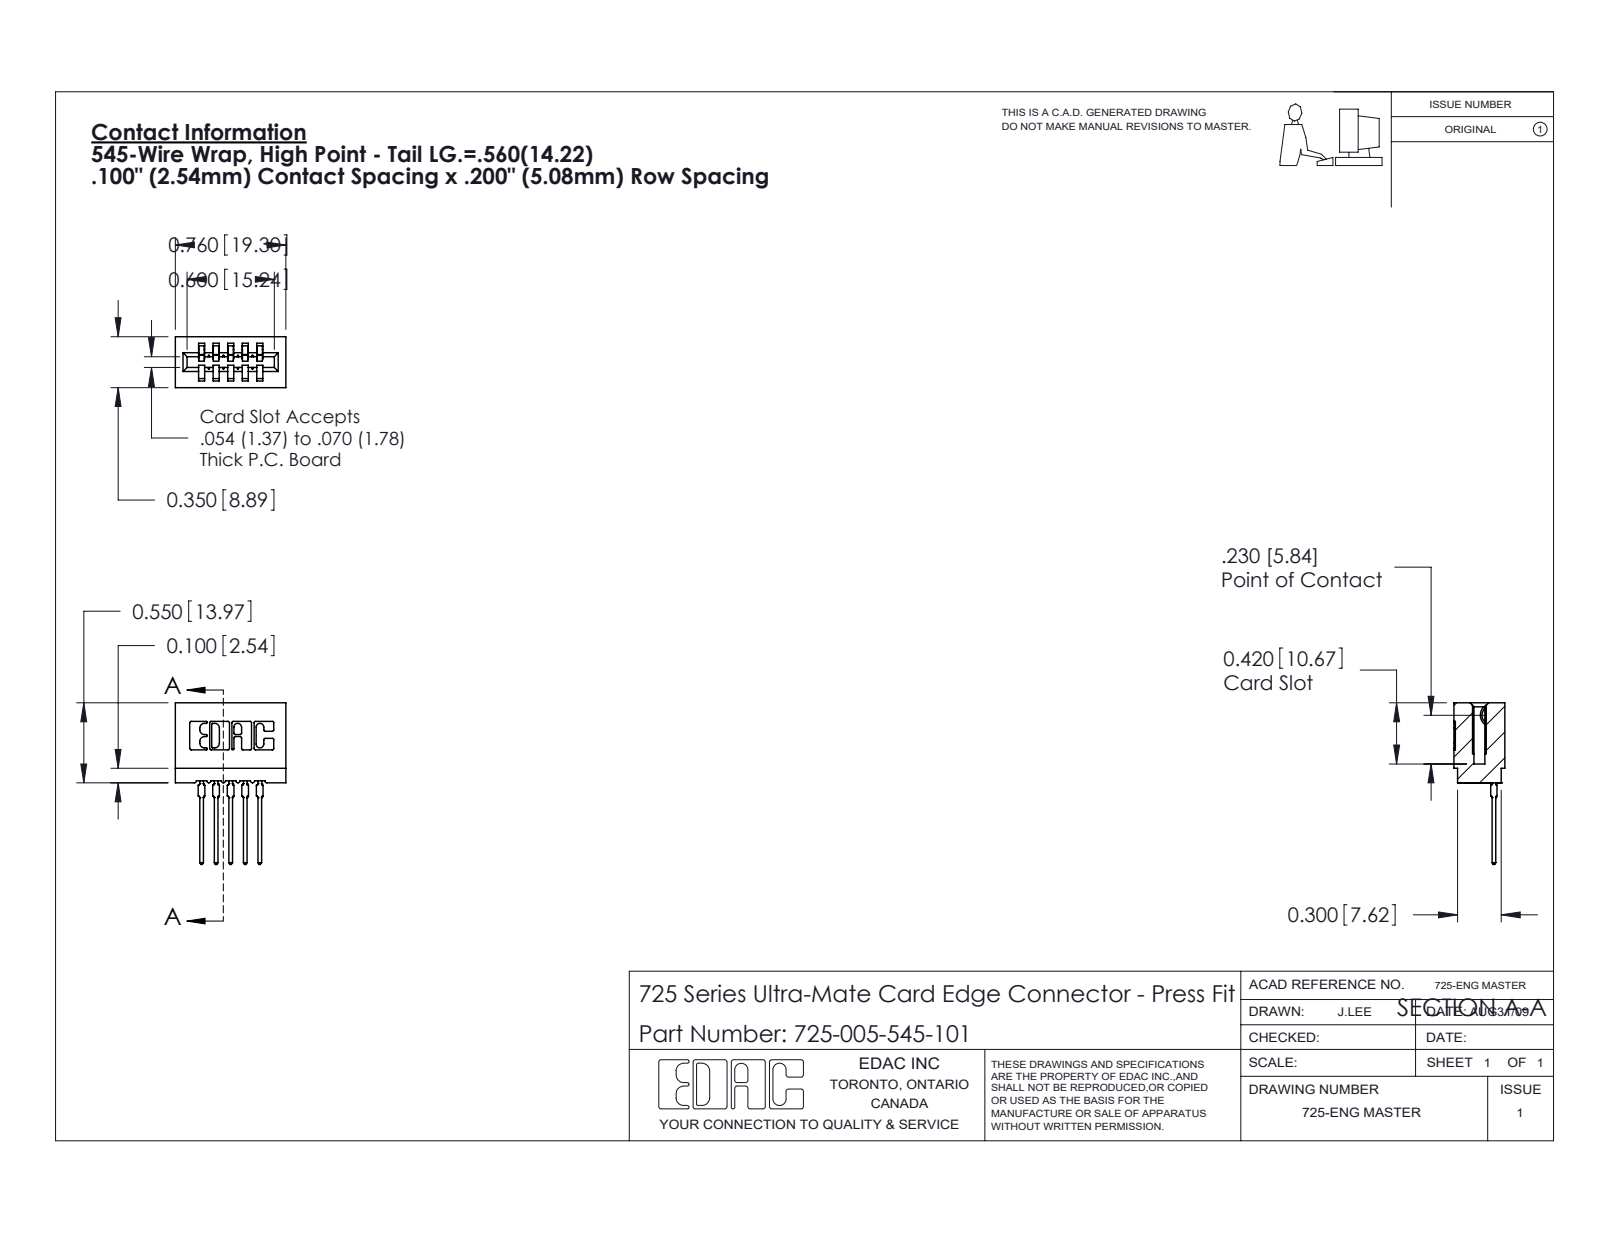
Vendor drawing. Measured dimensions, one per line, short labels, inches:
name: 725-005-545-101; 745-292-001_545; 725 Part_Insulator Option - 01
written by: SolidWorks 2020 (CONFIG_CONTROL_DESIGN)
unit: in
bodies: 6 solids, 655 faces (390 planar, 135 cylindrical, 130 other)
size: 1.111 × 0.76 × 0.35
volume: 0.103 in³; area: 4.105 in²
rounds: 22× R0.01, 10× R0.015, 10× R0.021, 6× R0.007, 6× R0.031, 4× R0.005, 4× R0.011, 3× R0.026
face distances: 0.1, 0.2, 0.042, 0.3, 0.142, 0.058, 0.242, 0.158, 0.212, 0.35
